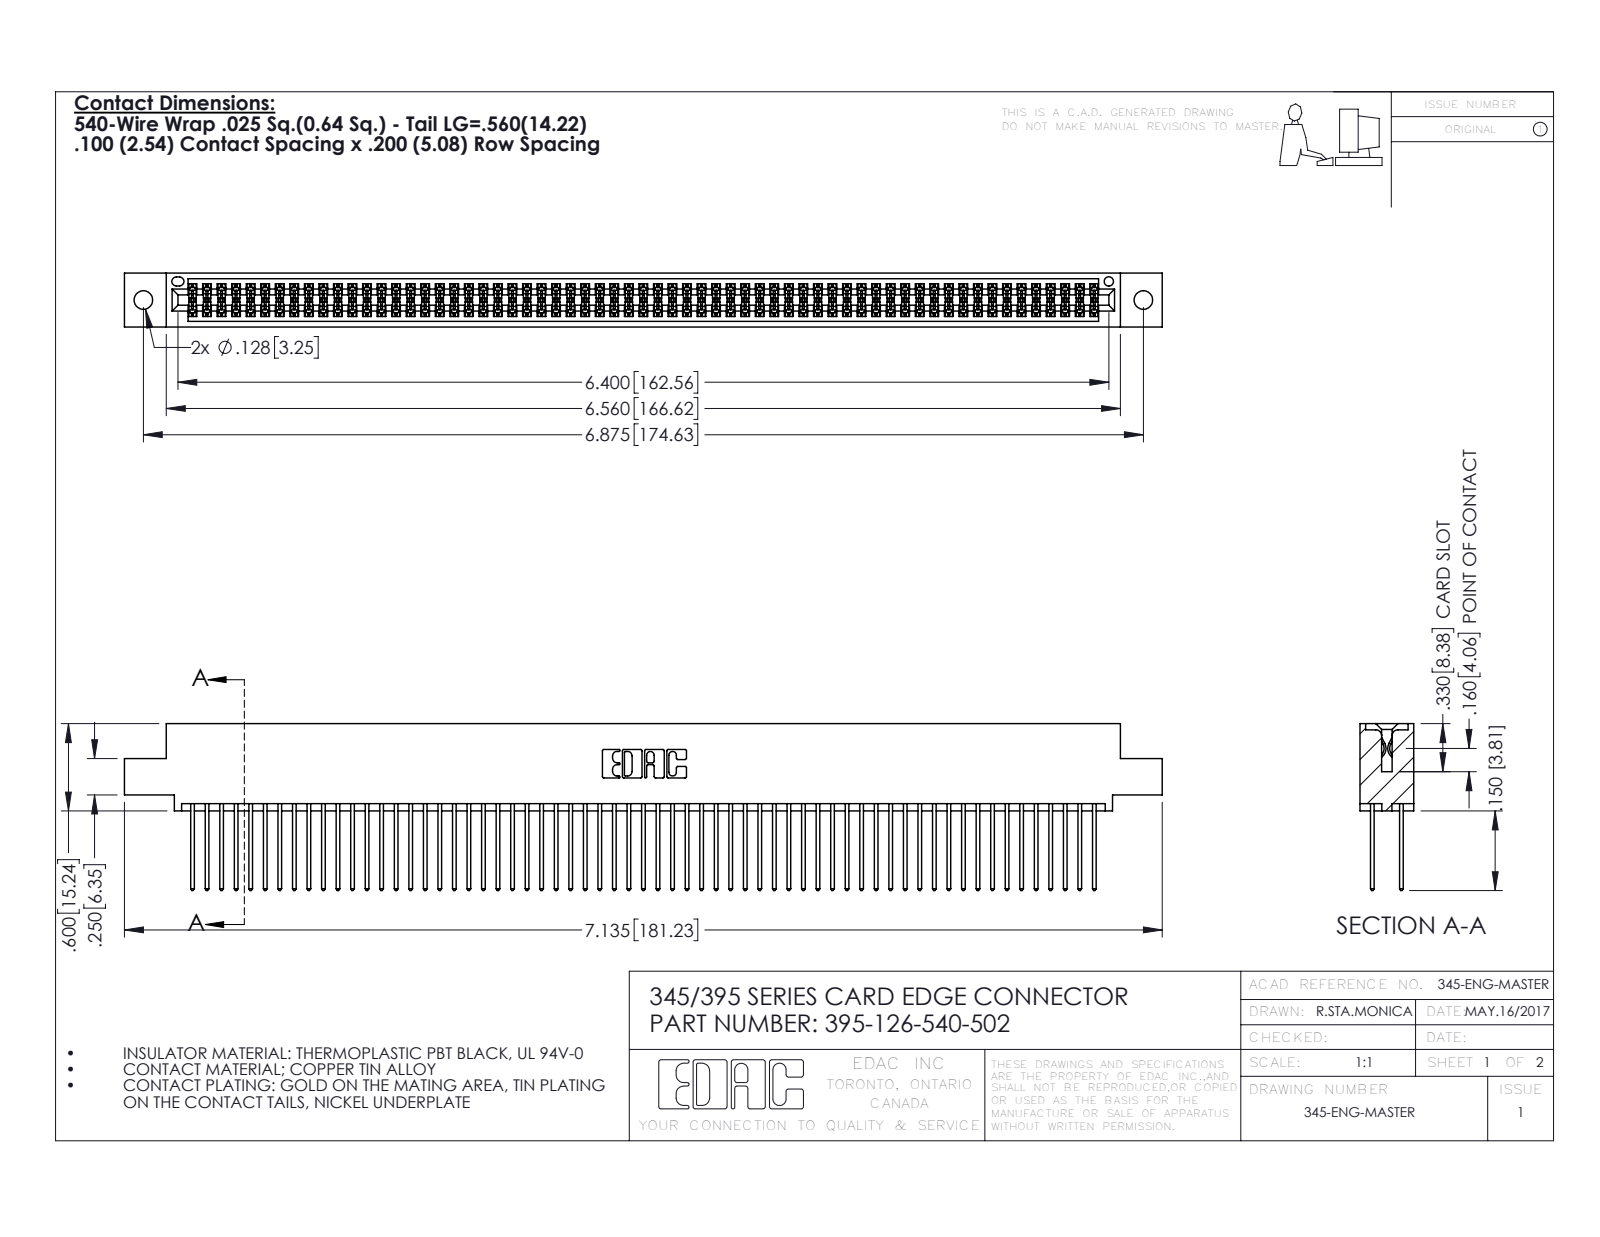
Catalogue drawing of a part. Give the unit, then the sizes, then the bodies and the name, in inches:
Units: inches
Overall size (bounding box): 7.135 × 1.147 × 0.37
Round holes (diameter × count): ⌀0.128 ×2, ⌀0.064 ×1
Partial cylindrical surfaces — rounded edges, fillets, slot ends (radius × count): R0.006 ×189, R0.01 ×126, R0.01 ×22, R0.007 ×6, R0.031 ×6, R0.026 ×3, R0.014 ×2, R0.019 ×2
Main face-to-face distances: 0.072, 0.298, 0.2, 0.098, 0.272, 0.025, 0.225, 0.37, 0.175, 0.149
Hole centre spacings: 0.27, 6.639, 6.875
Volume: 1.109 in³ · Surface area: 45.41 in²
Bodies: 127 solids, 6430 faces (4242 planar, 2188 cylindrical, 0 other)
Part name (STEP PRODUCT): 345-292-001_345-293-140; 395-126-540-502; 345 Part_0.110 Offset - 0.128 Dia
STEP written by: SolidWorks 2016 (CONFIG_CONTROL_DESIGN)
